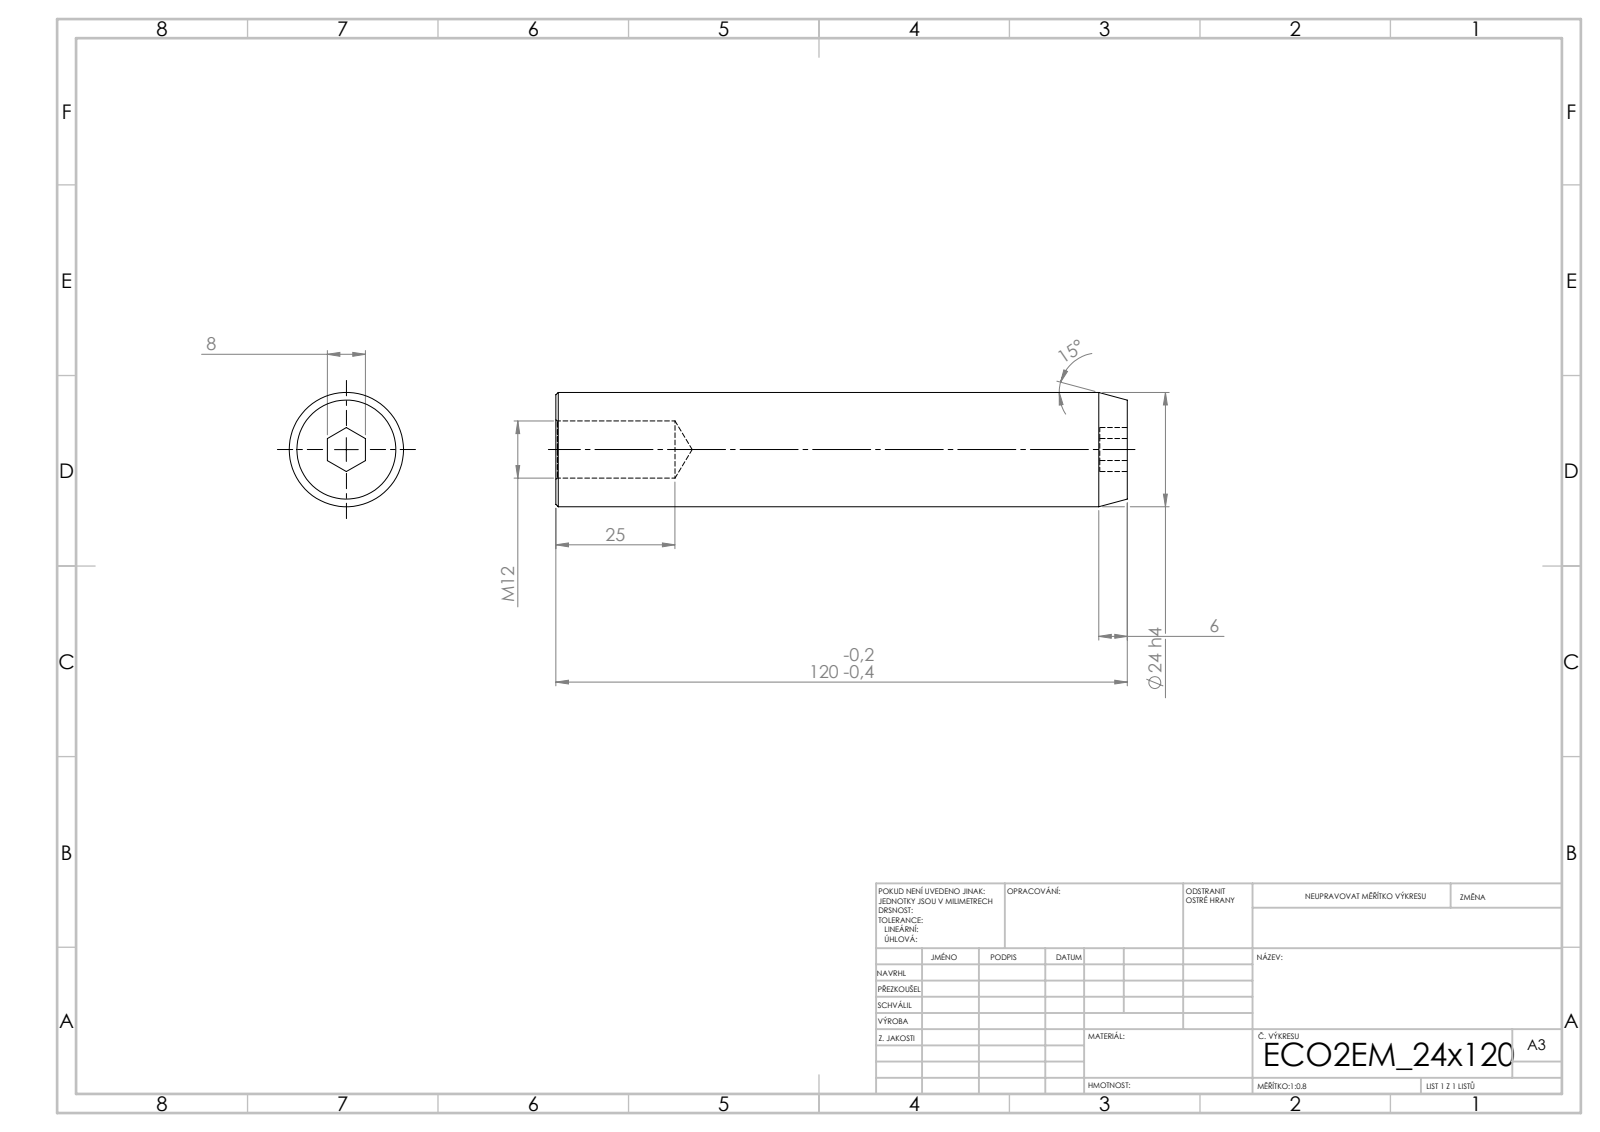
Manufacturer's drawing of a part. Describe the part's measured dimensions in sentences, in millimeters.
Its 3-D file was written by "SolidWorks 2019 (CONFIG_CONTROL_DESIGN)". It is 1 solid with 21 faces: 9 planar, 4 cylindrical and 8 other. Overall it measures 120 by 24 by 24 millimeters. Its volume is 50 644 cubic millimeters and its surface area 10 919 square millimeters. Round holes: 1 of diameter 12. Round bosses or shafts: 1 of diameter 24. The main face-to-face distances are 120, 8, 5.8, 114.2.
